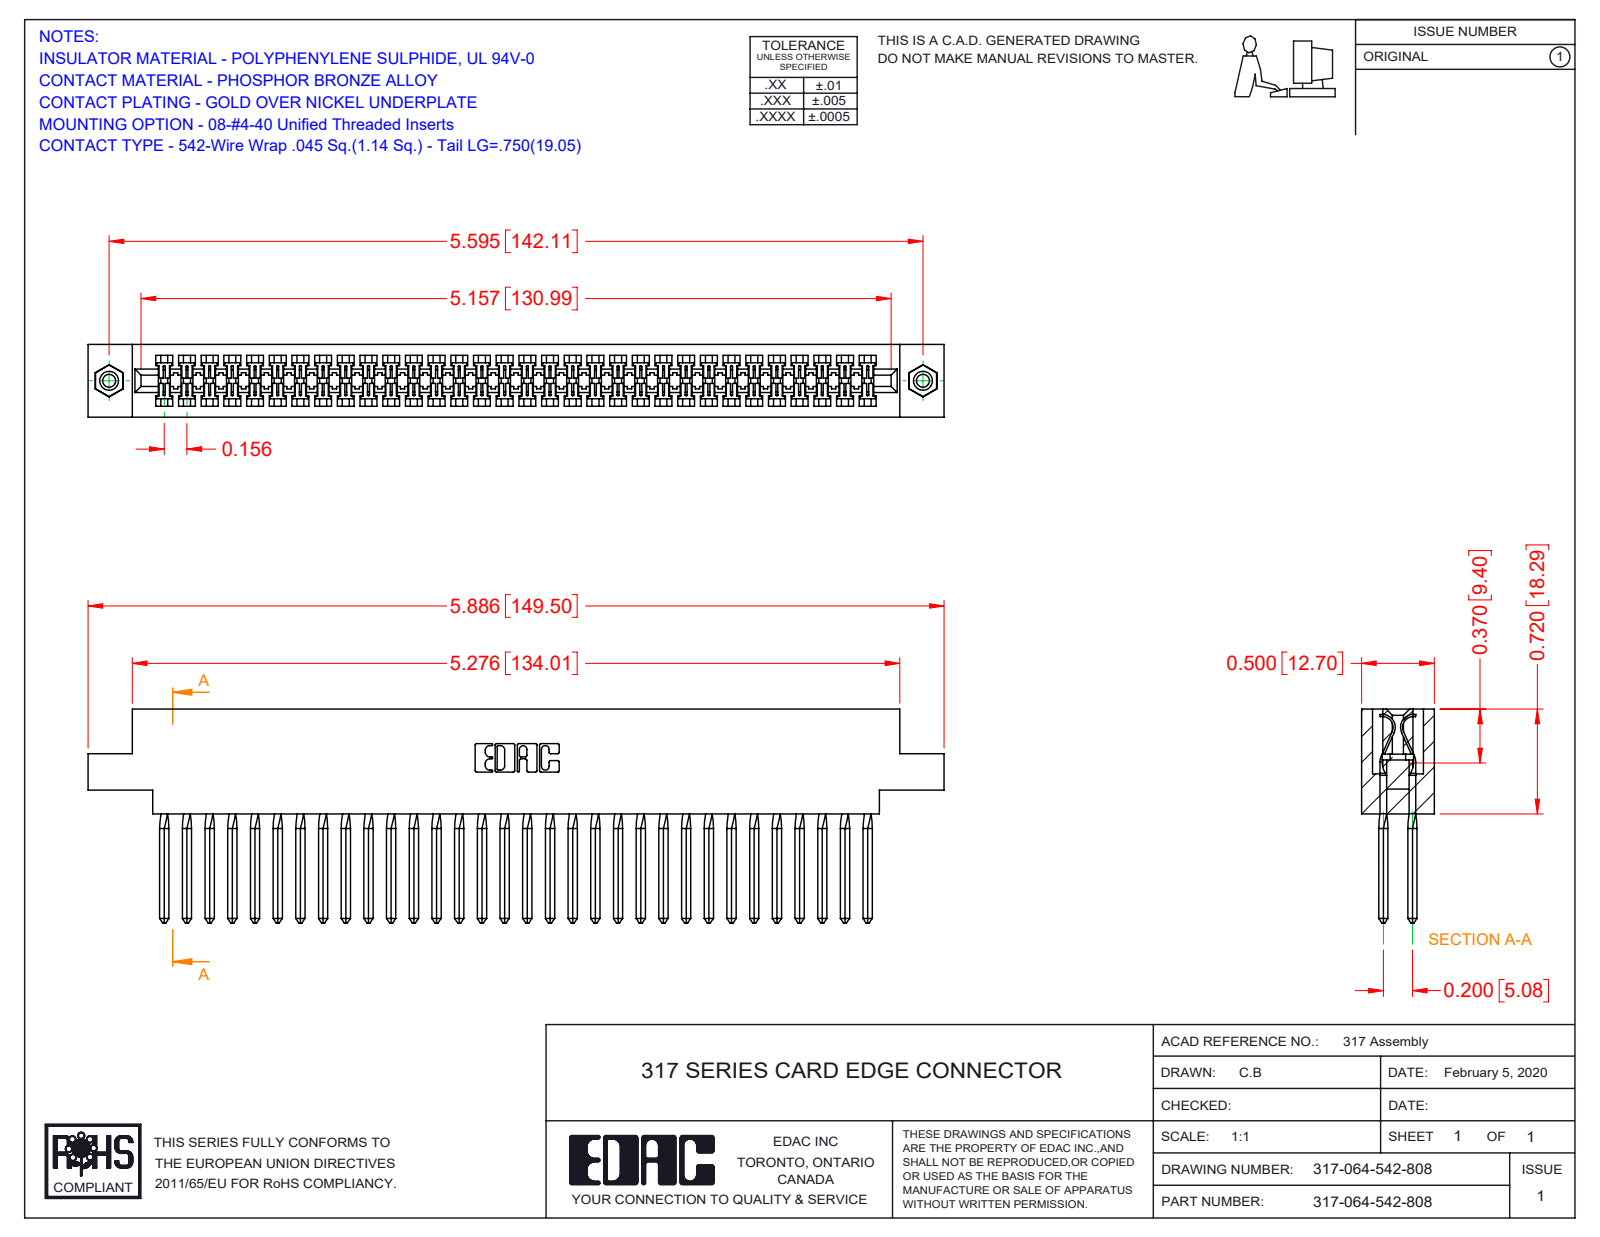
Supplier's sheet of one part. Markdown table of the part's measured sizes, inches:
| quantity | value |
| --- | --- |
| part name | 317 Part_.156 Dia - TI; 317-064-542-808; 317-290-003_542; 345-250-001_345-250-003-102 |
| STEP written by | SolidWorks 2016 (CONFIG_CONTROL_DESIGN) |
| units | inches |
| bodies | 67 solids, 3810 faces (3034 planar, 504 cylindrical, 272 other) |
| overall size | 5.886 × 1.47 × 0.5 |
| volume | 1.474 in³ |
| surface area | 51.61 in² |
| round holes (diameter × count) | 0.089 × 2, 0.125 × 2, 0.156 × 2 |
| round bosses / shafts (diameter × count) | 0.155 × 2 |
| partial cylindrical surfaces (radius × count) | 0.006 × 128, 0.01 × 22, 0.007 × 6, 0.031 × 6, 0.026 × 3, 0.074 × 2, 0.089 × 2, 0.1 × 2 |
| main face-to-face distances | 0.5, 0.075, 0.425, 0.35, 0.2, 0.116, 0.11, 0.046, 0.128, 0.372 |
| hole center spacings | 5.595 |
